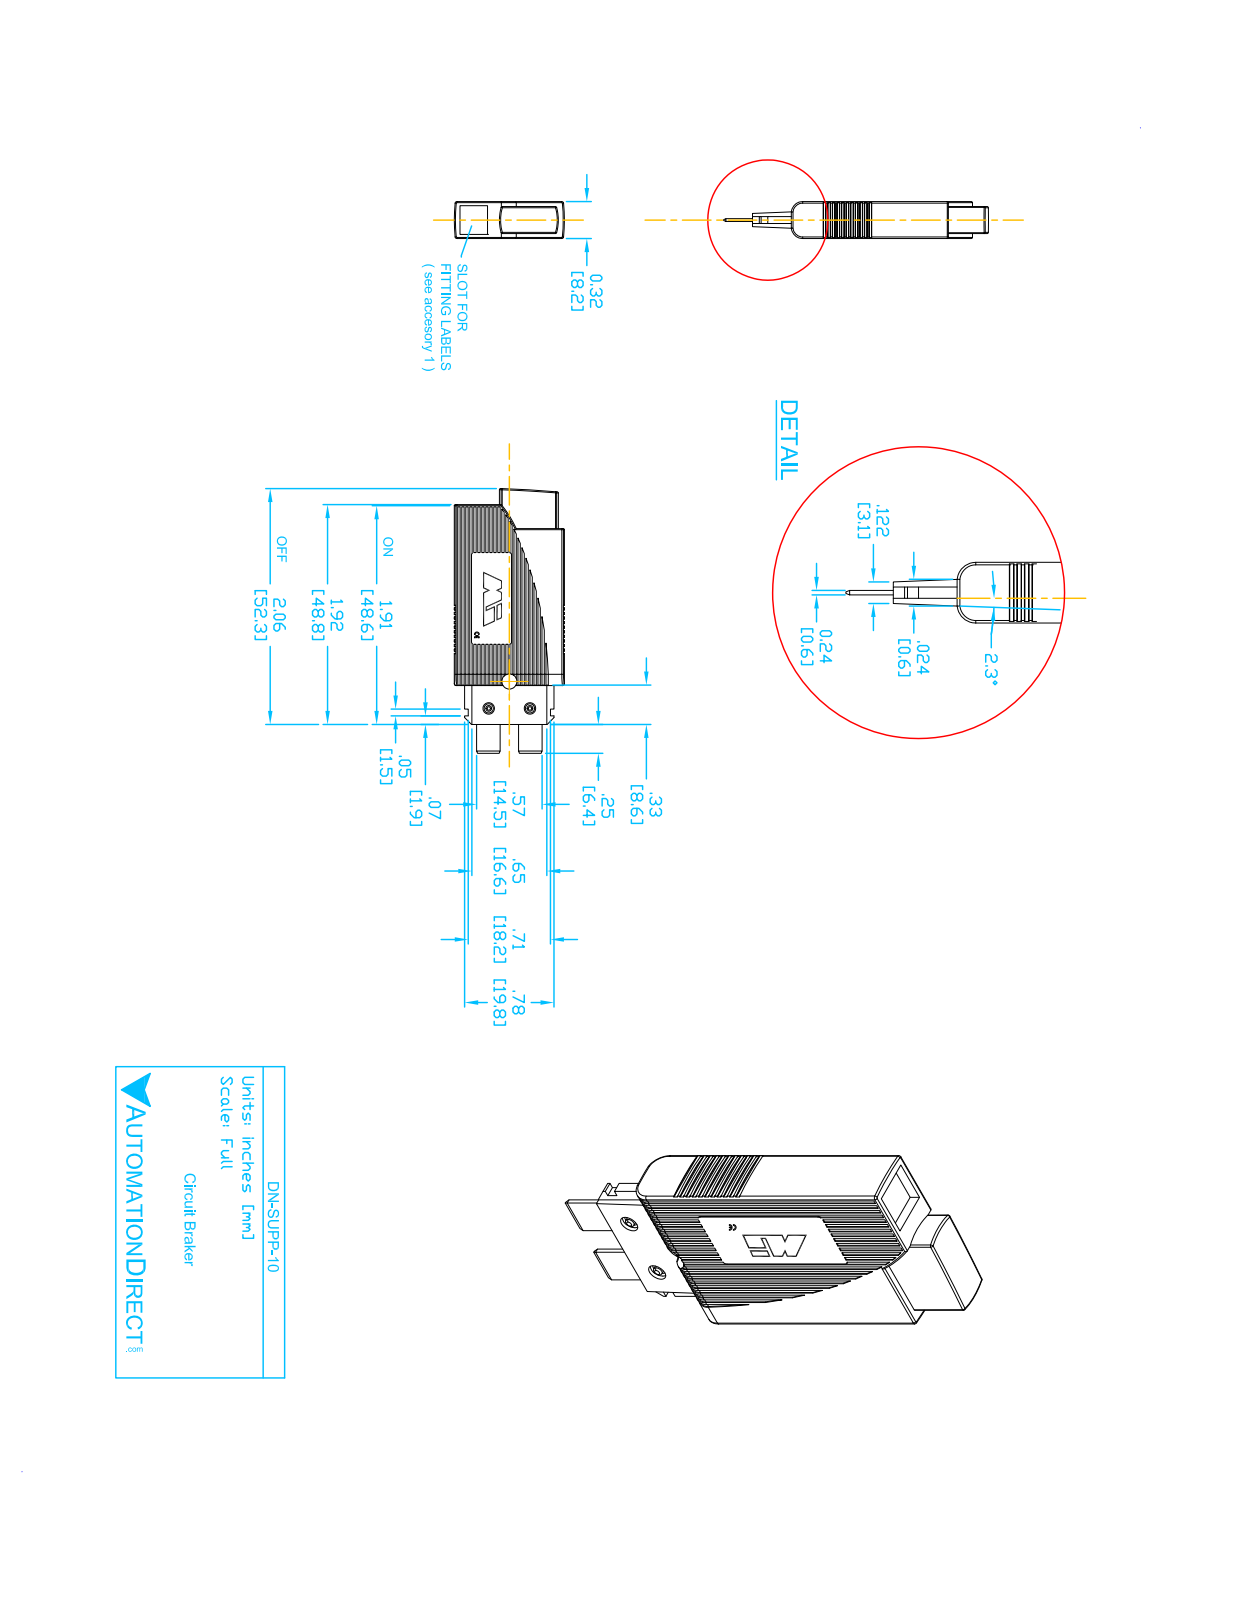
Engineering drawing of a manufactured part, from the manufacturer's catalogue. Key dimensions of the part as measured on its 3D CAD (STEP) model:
Part name (STEP PRODUCT): DN-SUPP-10
STEP written by: SolidWorks 2017 (AUTOMOTIVE_DESIGN)
Units: inches
Bodies: 1 solid, 95 faces (47 planar, 28 cylindrical, 20 other)
Overall size (bounding box): 2.18 × 0.961 × 0.323
Volume: 0.505 in³ · Surface area: 5.231 in²
Partial cylindrical surfaces — rounded edges, fillets, slot ends (radius × count): R0.012 ×21, R0.157 ×2, R2.165 ×1, R2.331 ×1, R2.362 ×1
Main face-to-face distances: 0.323, 0.961, 0.15, 0.173, 0.031, 0.291, 0.118, 0.142, 0.024, 0.14
